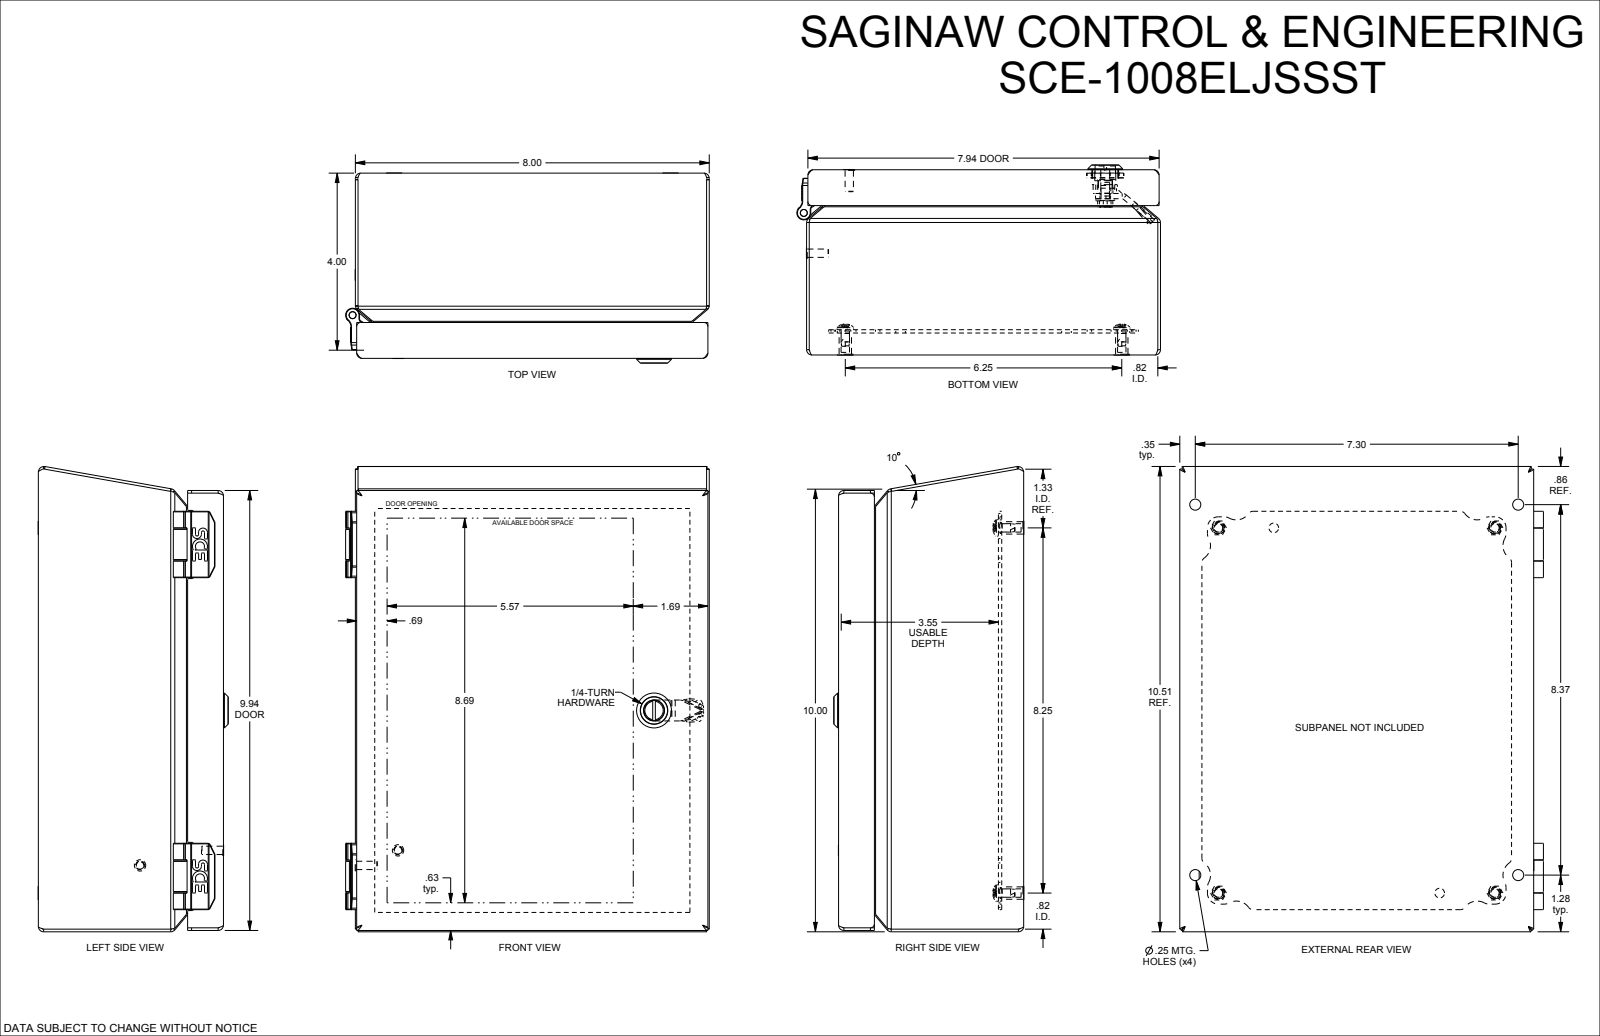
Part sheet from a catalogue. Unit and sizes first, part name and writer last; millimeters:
Units: millimetres
Overall size (bounding box): 266.8 × 208.8 × 109.1
Round holes (diameter × count): ⌀4.1 ×4, ⌀4.8 ×4, ⌀6.4 ×4, ⌀7.2 ×4, ⌀0.5 ×2, ⌀2.5 ×2, ⌀5.5 ×2, ⌀6.8 ×2, ⌀4 ×1, ⌀5 ×1, ⌀5.1 ×1, ⌀6.1 ×1
Round bosses / shafts (diameter × count): ⌀4.8 ×6, ⌀12.3 ×4, ⌀9.5 ×4, ⌀7.1 ×4, ⌀6 ×4, ⌀4.1 ×4, ⌀6.6 ×2, ⌀6.5 ×2
Partial cylindrical surfaces — rounded edges, fillets, slot ends (radius × count): R0.8 ×50, R0.2 ×24, R0.3 ×21, R6.4 ×13, R3.2 ×11, R0.3 ×10, R1.5 ×10, R1.6 ×8
Main face-to-face distances: 1.5, 1.5, 106.3, 104.8, 104.8, 103.3, 14.5, 13, 90.3, 91.8
Hole centre spacings: 190.5, 0.5, 16.8, 18.9, 31.8, 105.2, 127, 158.8
Volume: 453 100 mm³ · Surface area: 555 300 mm²
Bodies: 34 solids, 1454 faces (566 planar, 353 cylindrical, 535 other)
Part name (STEP PRODUCT): SCE-1008ELJSSST
STEP written by: SolidWorks 2021 (AUTOMOTIVE_DESIGN)
